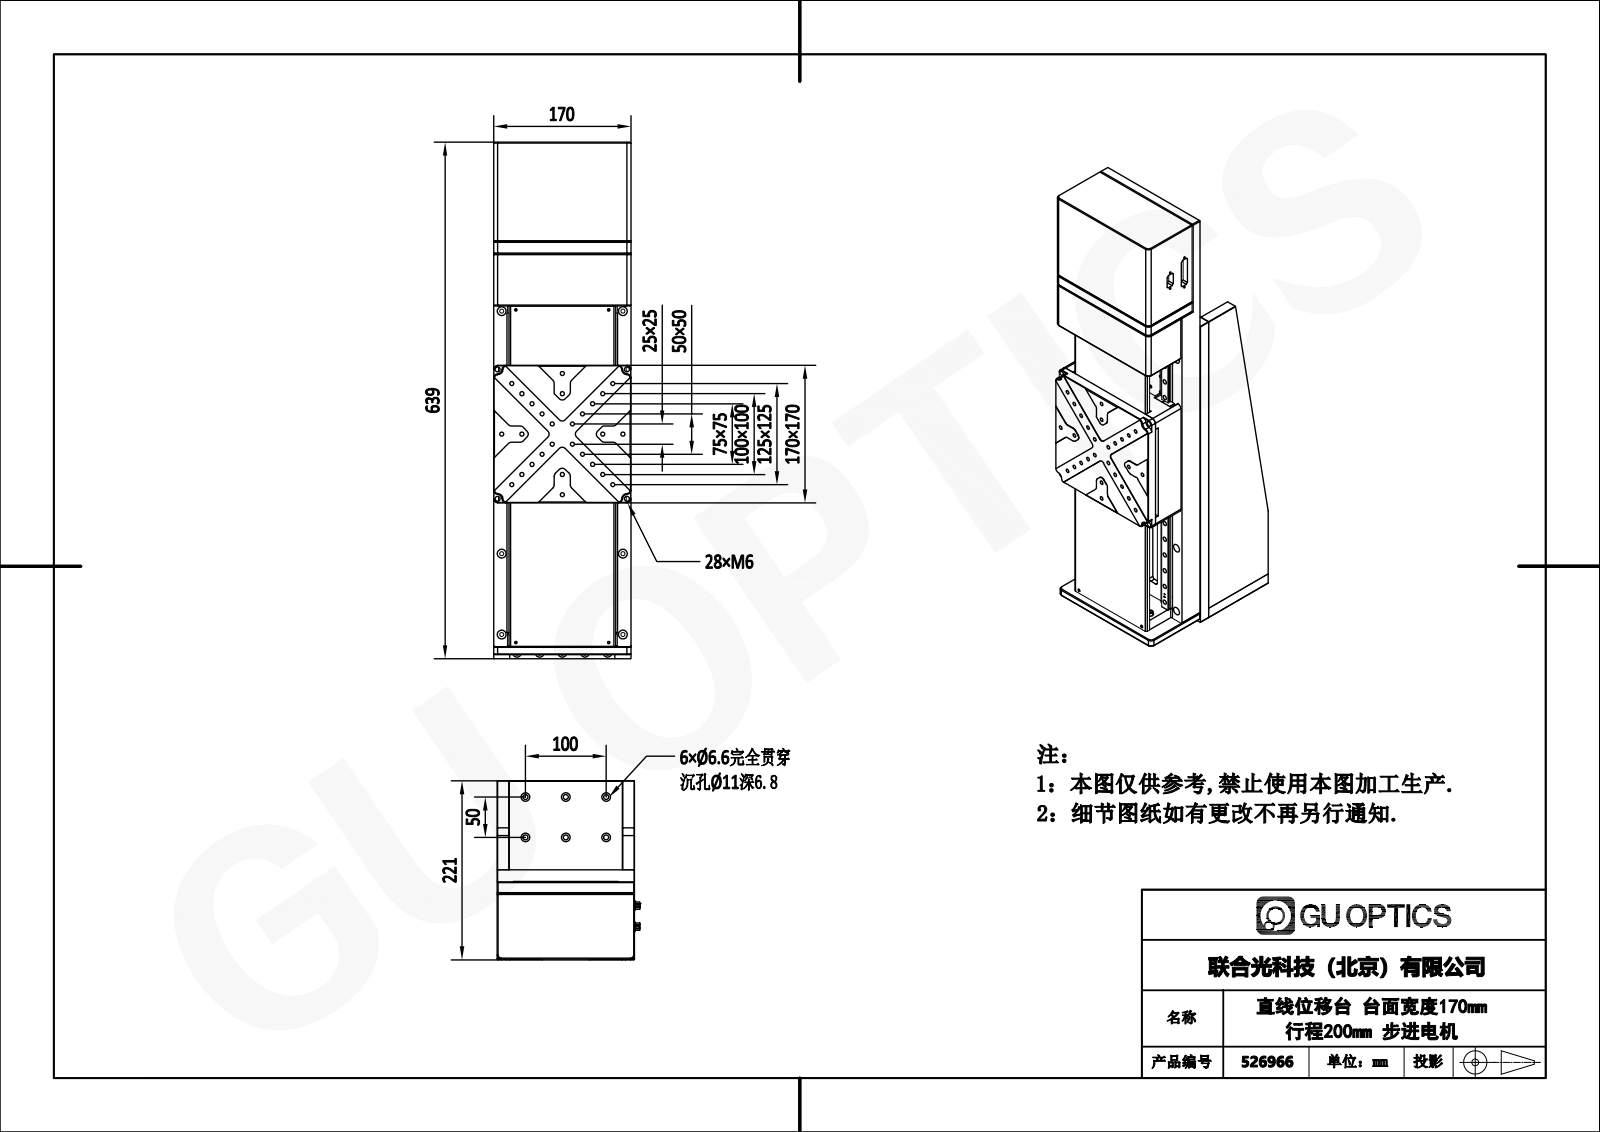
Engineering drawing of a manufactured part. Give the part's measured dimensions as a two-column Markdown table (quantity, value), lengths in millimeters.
| quantity | value |
| --- | --- |
| part name | FMSZ170S-200 |
| STEP written by | SolidWorks 2017 (CONFIG_CONTROL_DESIGN) |
| units | millimeters |
| bodies | 0 solids, 659 faces (311 planar, 298 cylindrical, 50 other) |
| overall size | 639 × 221.5 × 170 |
| round holes (diameter × count) | 5 × 32, 11 × 27, 6 × 22, 6.6 × 10, 2.5 × 4, 3.3 × 4, 8 × 4, 2.3 × 2, 2.4 × 2 |
| round bosses / shafts (diameter × count) | 9 × 4, 24 × 1 |
| partial cylindrical surfaces (radius × count) | 5 × 44, 2 × 11, 5.5 × 4, 1.25 × 2, 3 × 2 |
| main face-to-face distances | 15, 1, 170, 80, 155, 95.5, 48.5, 47.5, 0.5, 15.5 |
| hole center spacings | 50, 25, 100, 75, 138.07, 150, 300, 17.68 |
